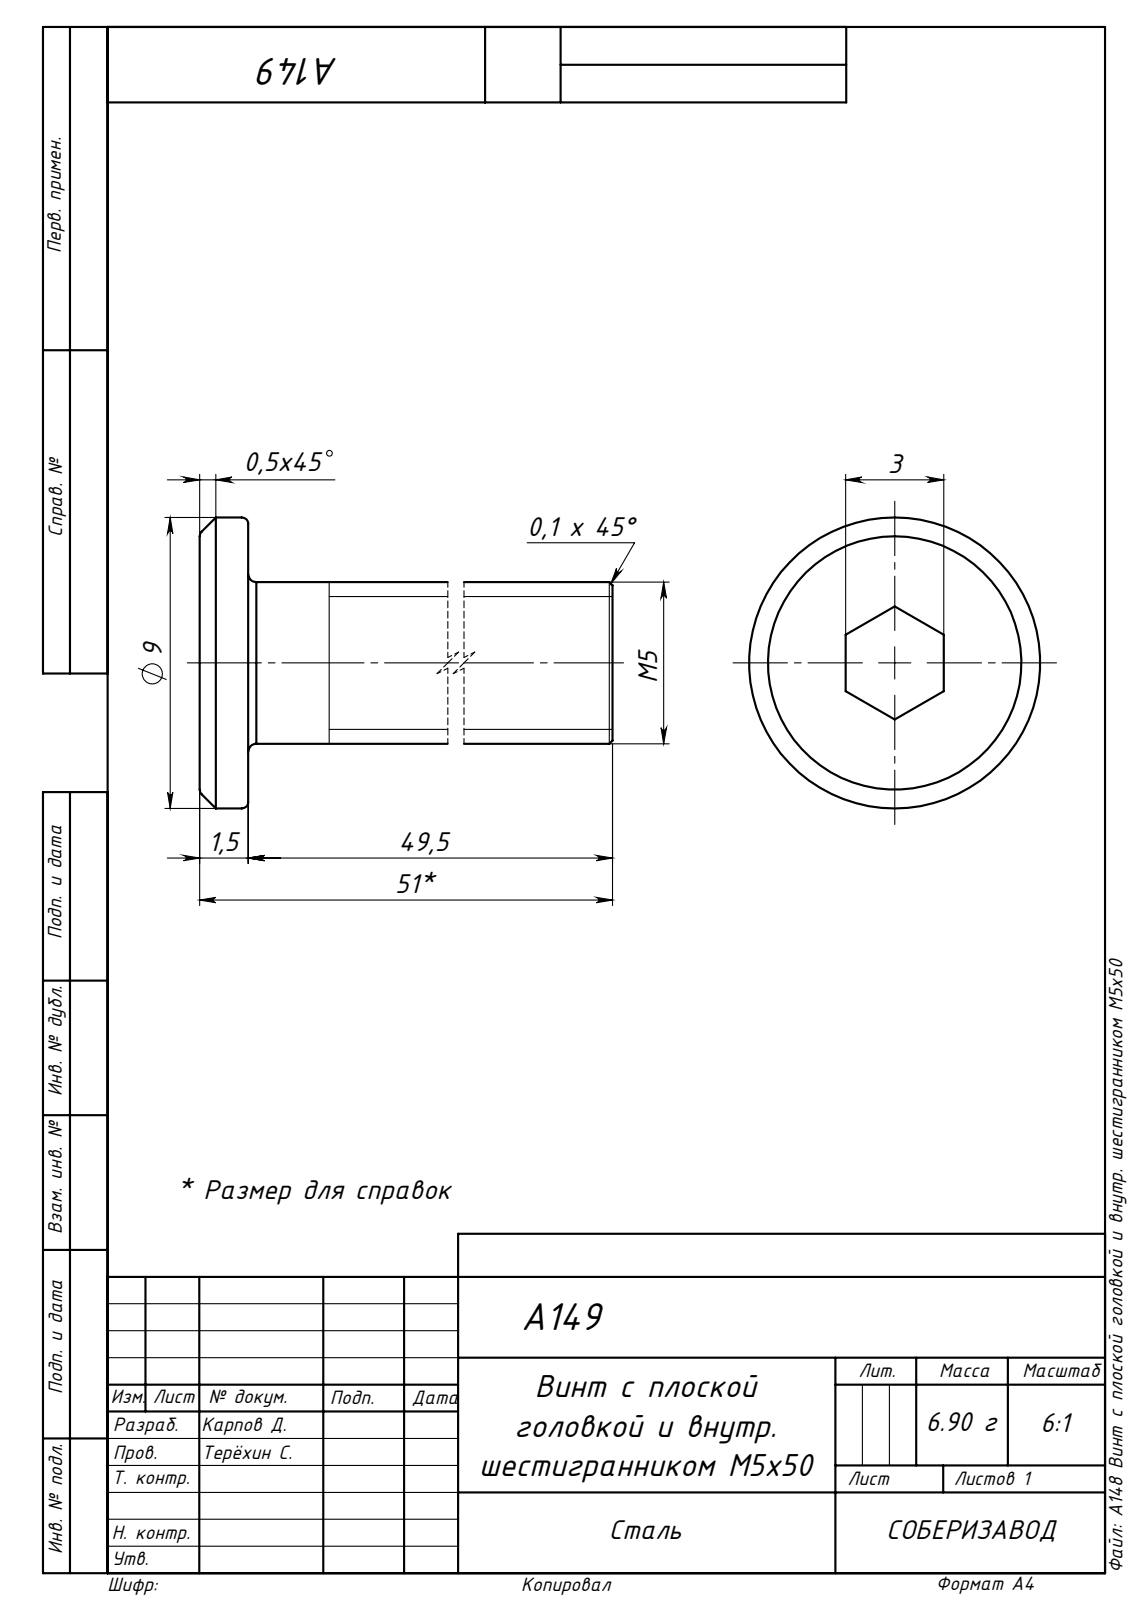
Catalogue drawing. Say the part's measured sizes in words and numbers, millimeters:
The part is named "A148 Винт с плоской головкой и внутр. шестигранником М5х50". Its 3-D file was written by "SolidWorks 2020 (AUTOMOTIVE_DESIGN)". It is 1 solid with 24 faces: 10 planar, 4 cylindrical and 10 other. Overall it measures 51 by 9 by 9 millimeters. Its volume is 1 052 cubic millimeters and its surface area 949 square millimeters. Round bosses or shafts: 1 of diameter 9, 1 of diameter 5. The main face-to-face distances are 1.5, 49.5, 51, 3.04.
